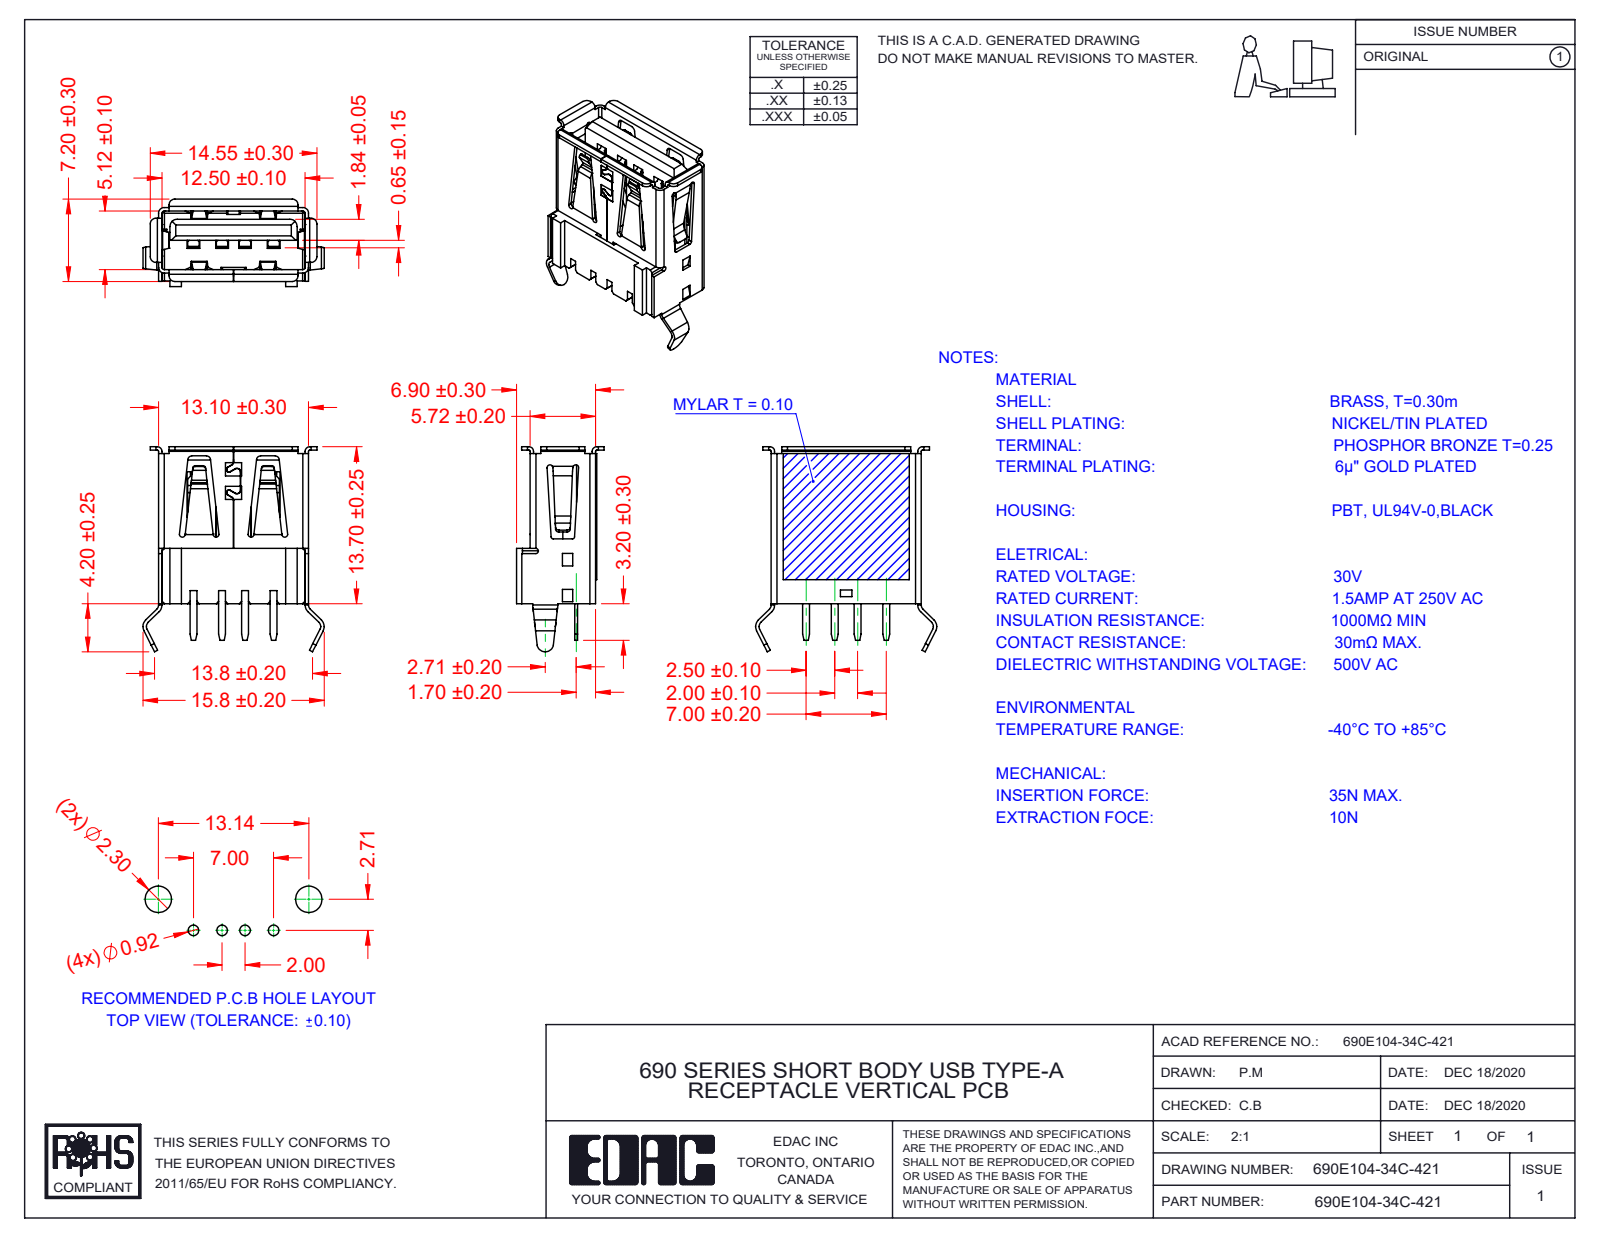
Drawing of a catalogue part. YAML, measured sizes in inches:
part_name: "Insulator 690E104-X4C-42X_Black; MYLAR 690E104-X4C-42X; Shell 690E104-X4C-42X; Contact 690E104-X4C-42X (+1 more)"
step_written_by: "SolidWorks 2020 (AUTOMOTIVE_DESIGN)"
units: inches
bodies: {solids: 7, faces: 742, planar: 558, cylindrical: 184, other: 0}
overall_size: [0.705, 0.623, 0.301]
volume: 0.035
surface_area: 3.312
partial_cylinders:
  - {radius: 0.008, count: 31}
  - {radius: 0.006, count: 18}
  - {radius: 0.02, count: 16}
  - {radius: 0.012, count: 11}
  - {radius: 0.01, count: 6}
  - {radius: 0.016, count: 5}
  - {radius: 0.004, count: 4}
  - {radius: 0.007, count: 4}
face_to_face_distances: [0.213, 0.016, 0.101, 0.142, 0.113, 0.098, 0.504, 0.185, 0.062, 0.066]
